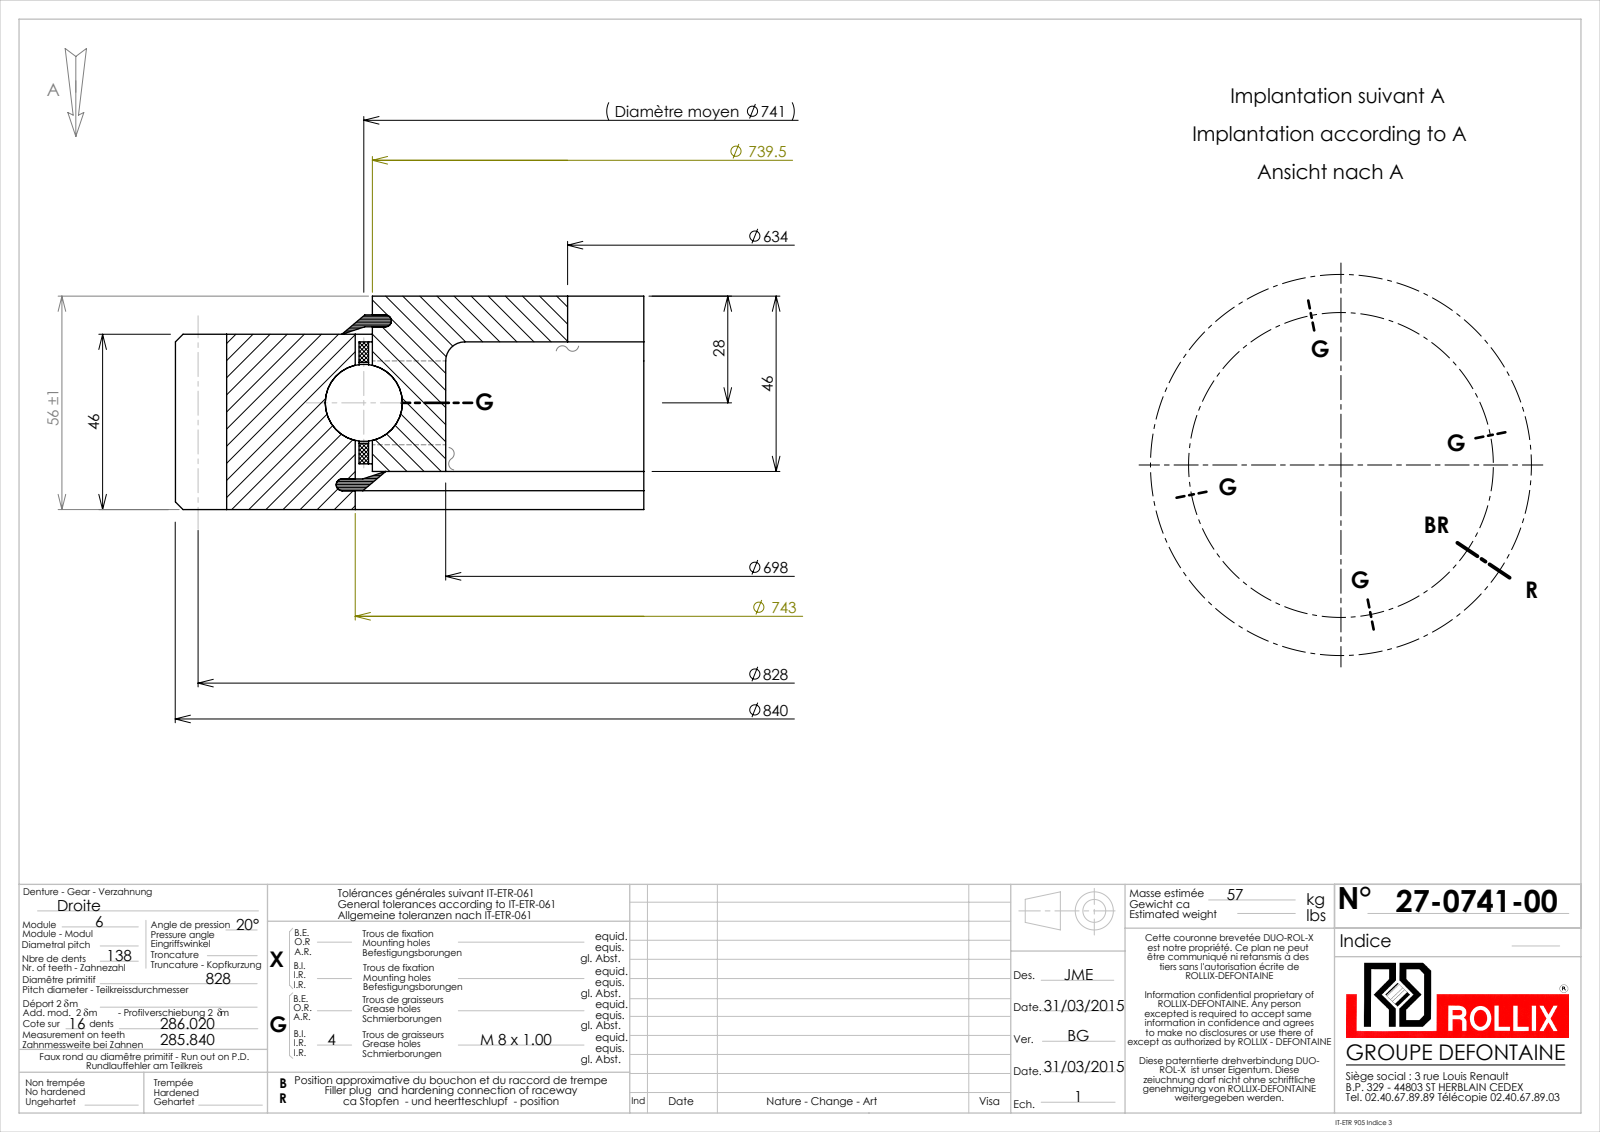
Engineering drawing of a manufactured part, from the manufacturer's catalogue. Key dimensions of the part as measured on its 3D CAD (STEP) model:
Part name (STEP PRODUCT): 21-0741-00
STEP written by: SolidWorks 2016 (CONFIG_CONTROL_DESIGN)
Units: millimetres
Bodies: 9 solids, 984 faces (329 planar, 309 cylindrical, 346 other)
Overall size (bounding box): 840 × 839.89 × 56
Volume: 7 043 000 mm³ · Surface area: 1 186 000 mm²
Round holes (diameter × count): ⌀7 ×4, ⌀634 ×1, ⌀698 ×1, ⌀745.5 ×1
Round bosses / shafts (diameter × count): ⌀8 ×4, ⌀736.5 ×1
Partial cylindrical surfaces — rounded edges, fillets, slot ends (radius × count): R406.5 ×1, R420 ×1
Main face-to-face distances: 10, 46, 56, 44, 2, 12, 34, 36, 4.95, 51.05
Hole centre spacings: 0.53
